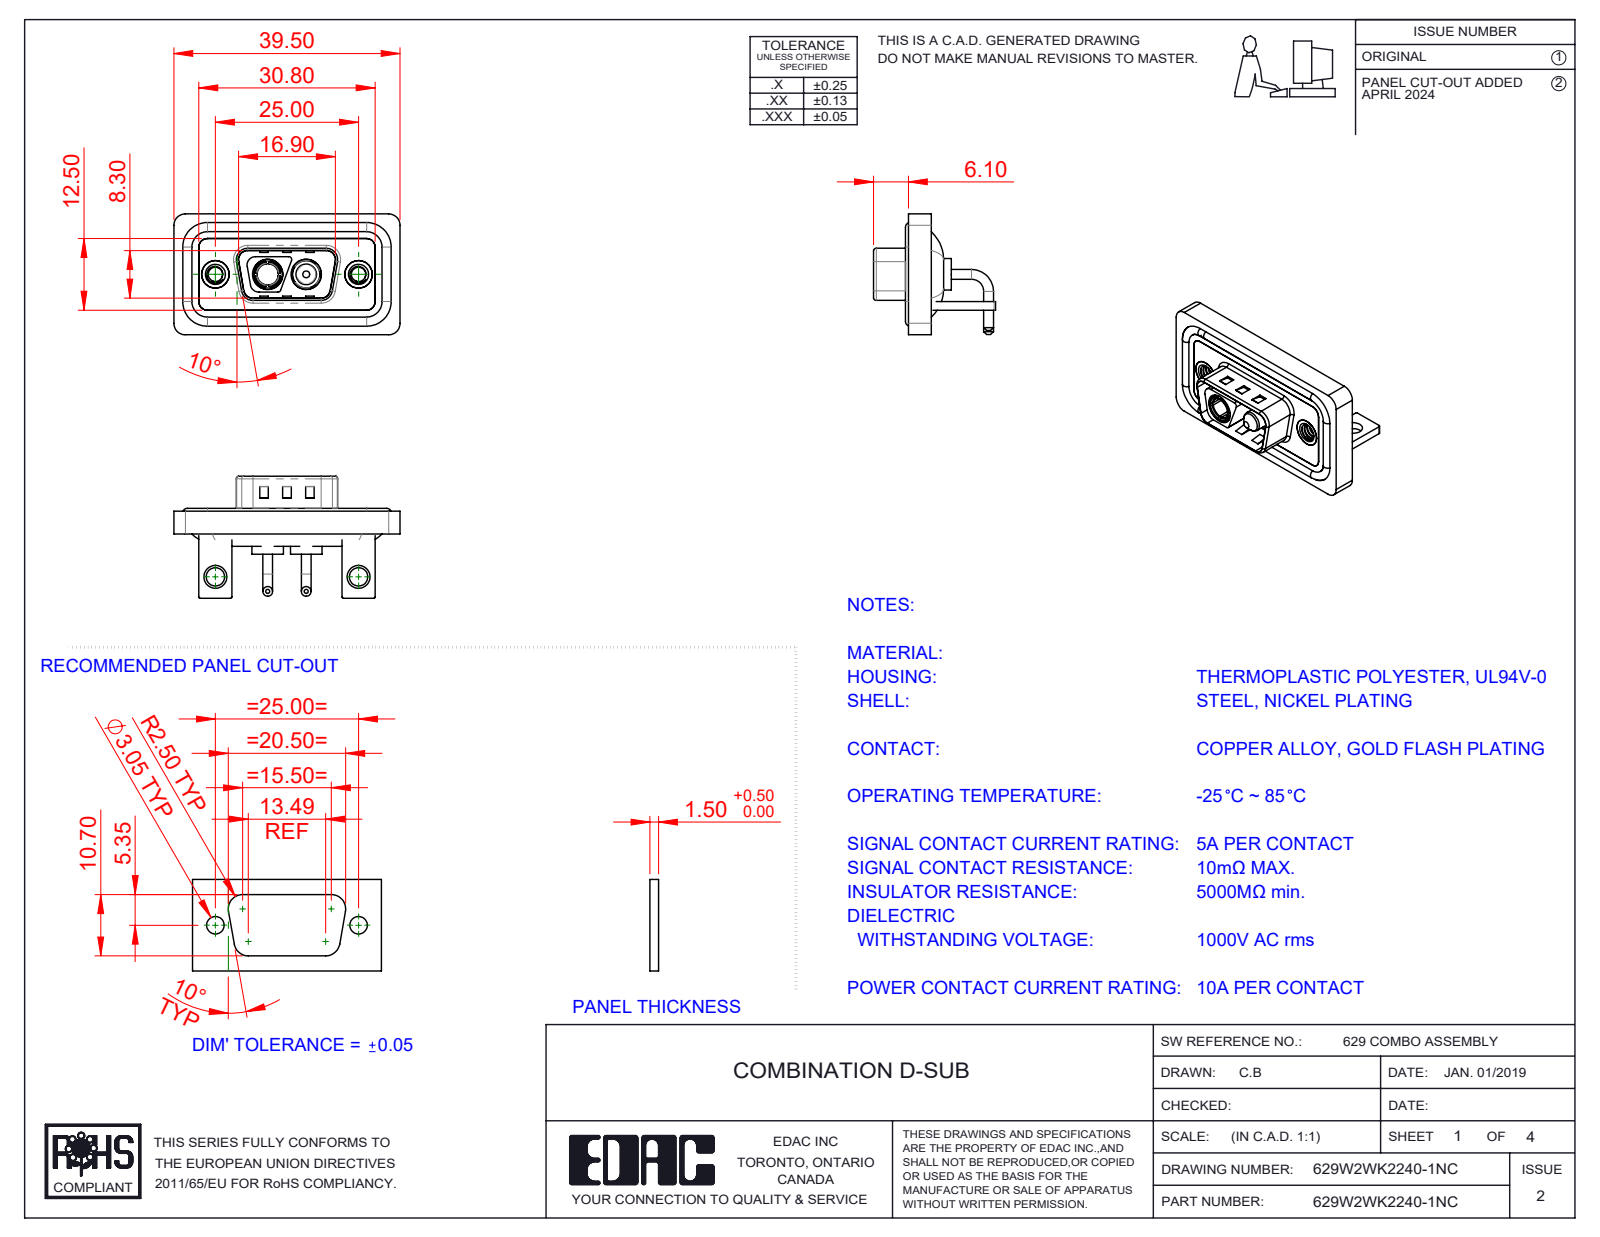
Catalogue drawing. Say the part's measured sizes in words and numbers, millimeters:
The part is named "629Combo Stabilizer Bracket; 629Combo Shell Rear_09 Contacts; 629Combo Waterproof Housing_09 Contacts; 629Combo Shell Front_09 Contacts (+5 more)". Its 3-D file was written by "SolidWorks 2023 (CONFIG_CONTROL_DESIGN)". It is 13 solids with 580 faces: 209 planar, 249 cylindrical and 122 other. Overall it measures 39.5 by 21.3 by 21.1 millimeters. Its volume is 4 836 cubic millimeters and its surface area 8 016 square millimeters. Round holes: 2 of diameter 2.5, 2 of diameter 3.2, 2 of diameter 4, 2 of diameter 4.8, 2 of diameter 4.85, 2 of diameter 5, 2 of diameter 5.3, 1 of diameter 3.7. Round bosses or shafts: 4 of diameter 1.7, 4 of diameter 1.6, 2 of diameter 5.5, 2 of diameter 5.2, 2 of diameter 4.9, 2 of diameter 4.75, 2 of diameter 3.75, 1 of diameter 4.96. Partial cylindrical surfaces (rounded edges, fillets, slot ends): 20 of radius 1.5, 19 of radius 2, 16 of radius 0.25, 11 of radius 0.5, 8 of radius 1.6, 4 of radius 0.6, 4 of radius 0.65, 4 of radius 0.9. The main face-to-face distances are 0.4, 1.5, 2.9, 0.8, 1.1, 1.2, 2.1, 1.6, 3.7, 2.5. The hole center spacings are 9.14, 15.86, 25, 6.72.
